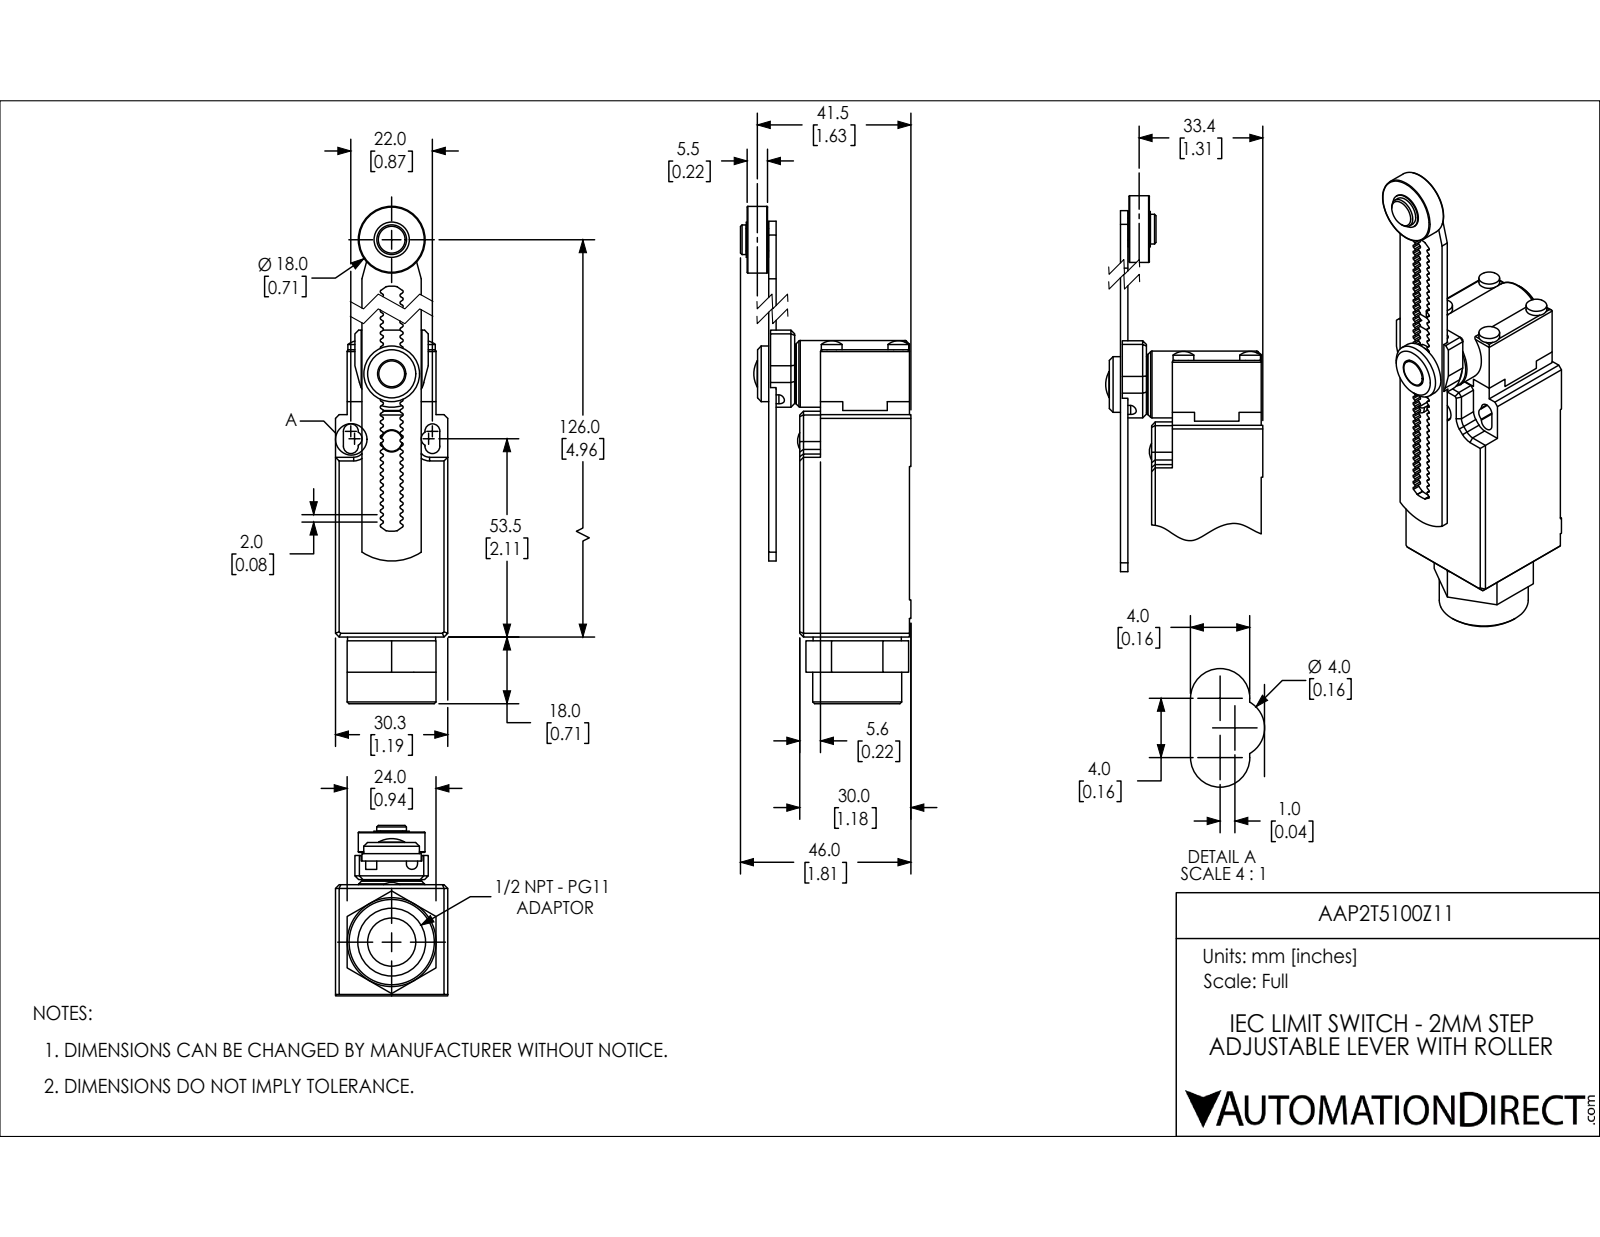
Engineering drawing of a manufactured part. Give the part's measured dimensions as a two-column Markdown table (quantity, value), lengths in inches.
| quantity | value |
| --- | --- |
| part name | AAP2T5100Z11 |
| STEP written by | SolidWorks 2018 (AUTOMOTIVE_DESIGN) |
| units | inches |
| bodies | 7 solids, 836 faces (345 planar, 447 cylindrical, 44 other) |
| overall size | 6.024 × 1.811 × 1.193 |
| volume | 4.493 in³ |
| surface area | 37.41 in² |
| round holes (diameter × count) | 0.236 × 1, 0.299 × 1, 0.433 × 1, 0.512 × 1, 0.669 × 1, 0.72 × 1, 0.74 × 1, 0.748 × 1 |
| round bosses / shafts (diameter × count) | 0.22 × 5, 0.709 × 2, 0.945 × 1, 0.937 × 1, 0.724 × 1, 0.591 × 1, 0.374 × 1, 0.315 × 1 |
| partial cylindrical surfaces (radius × count) | 0.016 × 166, 0.079 × 6, 0.008 × 4, 0.02 × 4, 0.118 × 4, 0.256 × 2, 0.059 × 1, 0.181 × 1 |
| main face-to-face distances | 0.079, 1.193, 0.252, 1.417, 1.165, 1.496, 0.331, 0.945, 0.124, 1.069 |
| hole center spacings | 0.713 |
